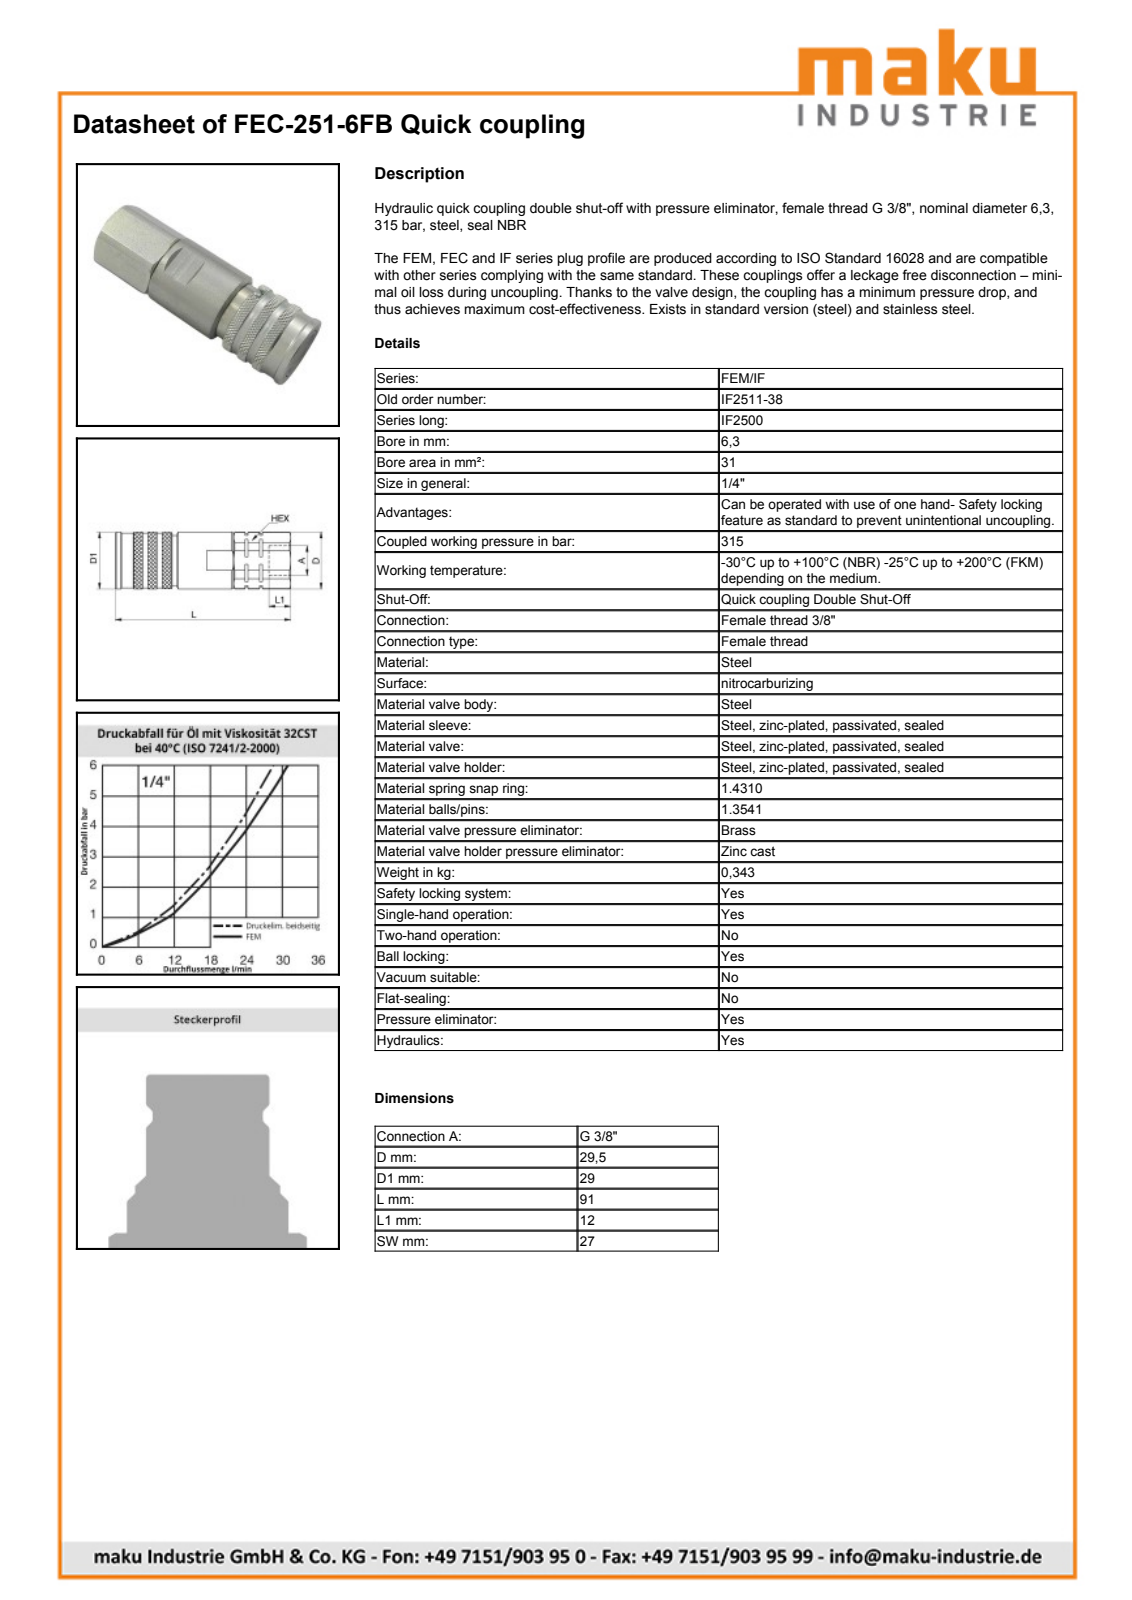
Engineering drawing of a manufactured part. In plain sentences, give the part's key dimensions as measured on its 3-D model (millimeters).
The part is named "FEC-251-6FB". Its 3-D file was written by "SolidWorks 2009 (AUTOMOTIVE_DESIGN)". It is 1 solid with 142 faces: 37 planar, 53 cylindrical and 52 other. Overall it measures 90.85 by 29.5 by 29 millimeters. Its volume is 54 151 cubic millimeters and its surface area 12 149 square millimeters. Round holes: 1 of diameter 2, 1 of diameter 9.65, 1 of diameter 14.95, 1 of diameter 16.2, 1 of diameter 20.9, 1 of diameter 22.38, 1 of diameter 24.2. Round bosses or shafts: 1 of diameter 29, 1 of diameter 27.5, 1 of diameter 25.05, 1 of diameter 24, 1 of diameter 22, 1 of diameter 16.1, 1 of diameter 9.6. Partial cylindrical surfaces (rounded edges, fillets, slot ends): 2 of radius 0.5, 1 of radius 10.11, 1 of radius 14.75. The main face-to-face distances are 27, 0.5, 90.85, 26.5, 90.35, 12.9, 77.45, 77.95, 15.2, 62.25.
